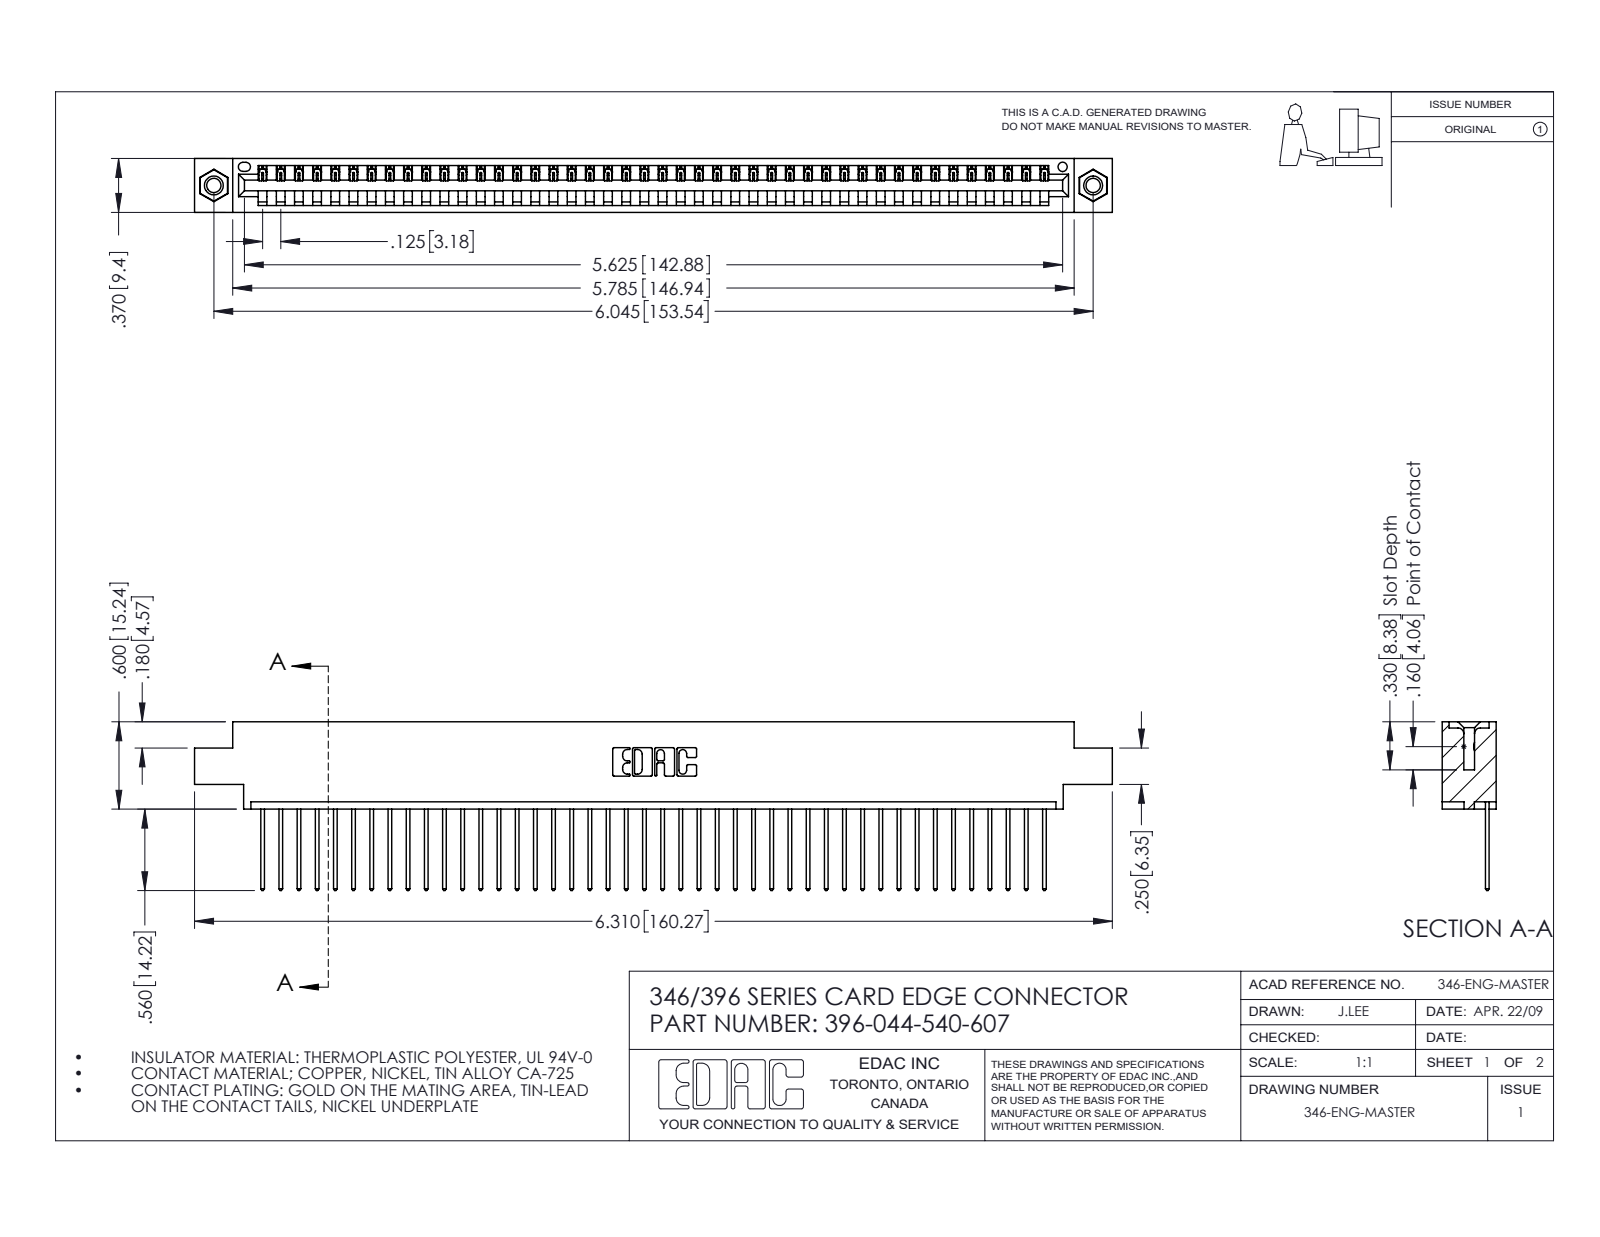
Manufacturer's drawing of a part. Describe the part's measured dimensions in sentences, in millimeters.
The part is named "396-044-540-607; 345-250-001_345-250-005-103; 346 Part_0.170 Offset - 0.156 Dia-TI; 345-292-001_345-293-140". Its 3-D file was written by "SolidWorks 2016 (CONFIG_CONTROL_DESIGN)". It is 47 solids with 2738 faces: 1872 planar, 850 cylindrical and 16 other. Overall it measures 160.3 by 29.5 by 9.4 millimeters. Its volume is 15 200 cubic millimeters and its surface area 19 710 square millimeters. Round holes: 2 of diameter 2.5, 2 of diameter 3.2, 2 of diameter 4, 1 of diameter 1.6. Round bosses or shafts: 2 of diameter 3.9. Partial cylindrical surfaces (rounded edges, fillets, slot ends): 88 of radius 0.2, 88 of radius 0.3, 22 of radius 0.3, 6 of radius 0.2, 6 of radius 0.8, 3 of radius 0.7, 2 of radius 0.8, 2 of radius 1. The main face-to-face distances are 1.2, 8.2, 9.4, 6.4, 1.8, 7.6, 0.6, 5.6, 3.8, 2.5. The hole center spacings are 6.2, 148.2, 153.5.
